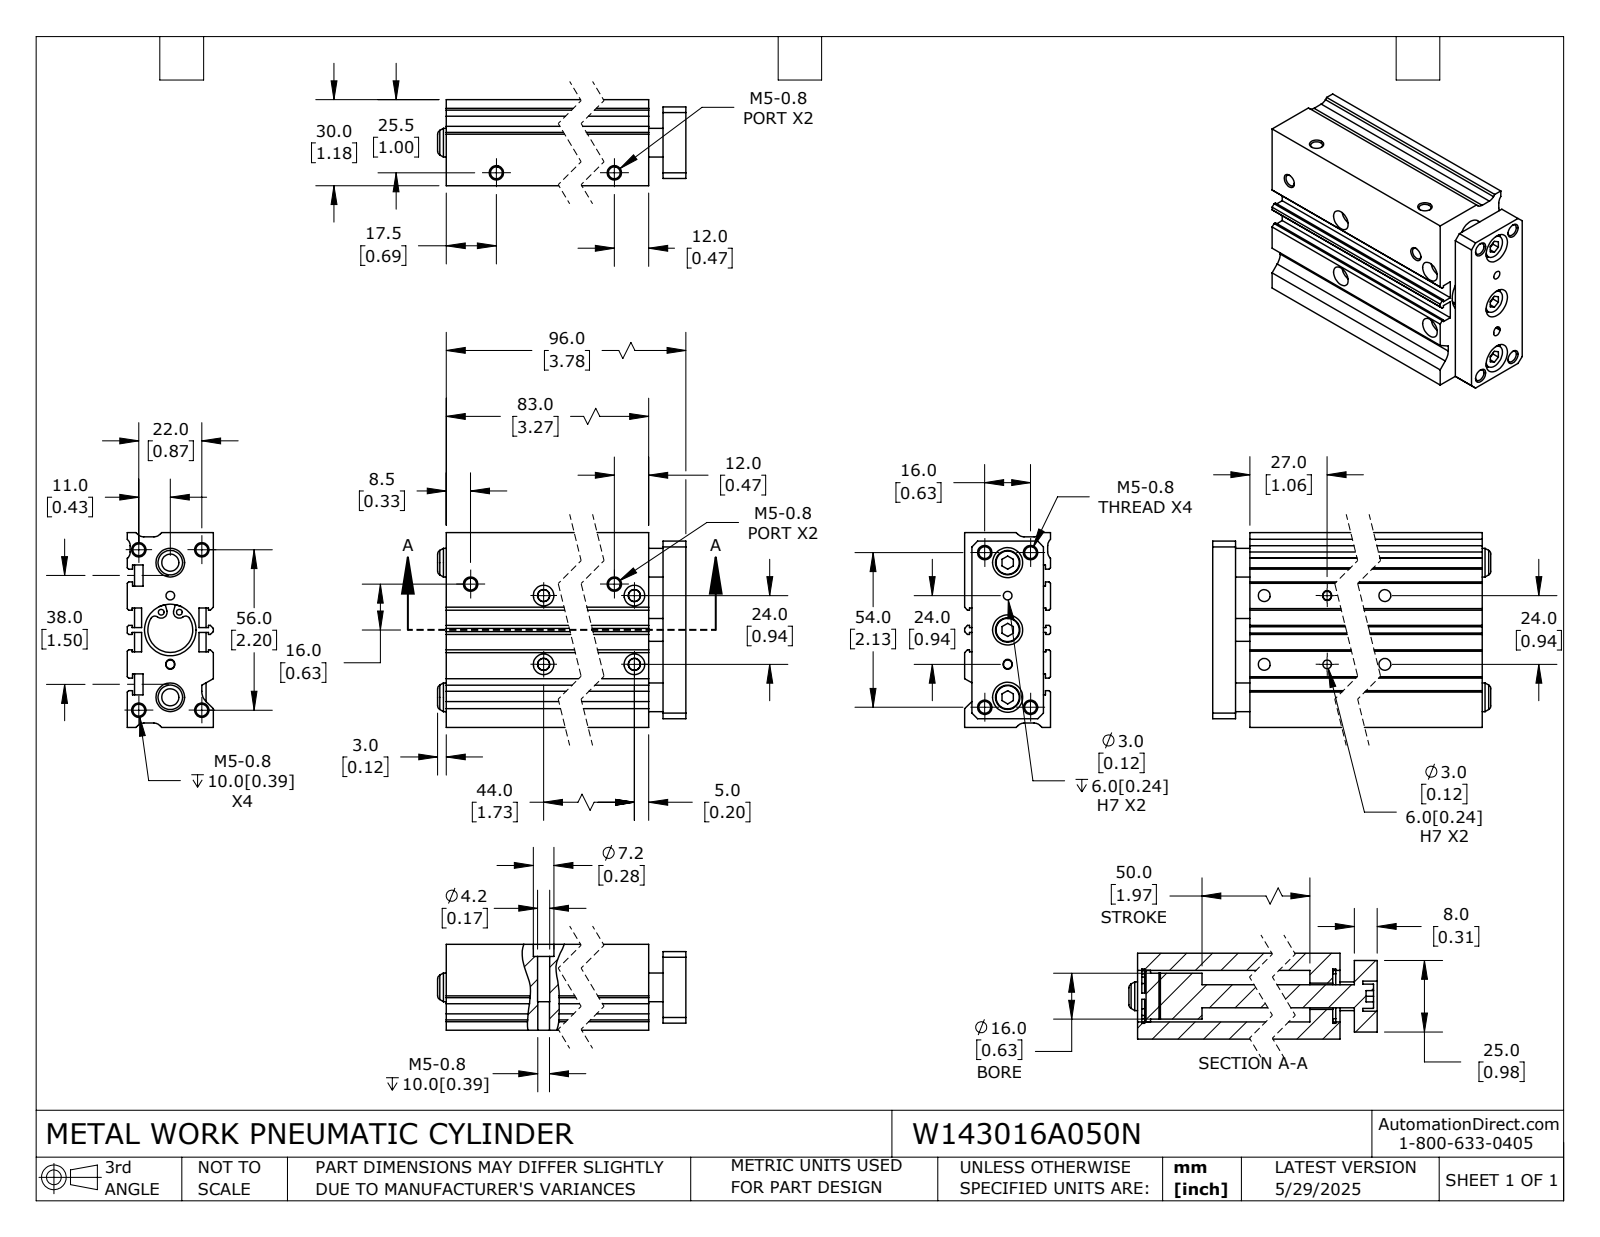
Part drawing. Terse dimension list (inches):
name: W143016A050_ROD; W143016A050_BODY; W143016A050N
written by: SolidWorks 2024 (CONFIG_CONTROL_DESIGN)
unit: in
bodies: 5 solids, 344 faces (169 planar, 137 cylindrical, 38 other)
size: 3.898 × 2.677 × 1.181
volume: 8.856 in³; area: 84.52 in²
holes: 16× ⌀0.163, 4× ⌀0.079, 4× ⌀0.118, 4× ⌀0.165, 4× ⌀0.283, 3× ⌀0.413, 2× ⌀0.394, 1× ⌀0.362, 1× ⌀0.618, 1× ⌀0.709
bosses: 3× ⌀0.335, 2× ⌀0.748, 1× ⌀0.63, 1× ⌀0.315
rounds: 6× R0.118, 4× R0.059, 4× R0.062, 4× R0.081, 1× R0.197
face distances: 0.197, 1.181, 0.984, 0.098, 0.059, 2.677, 0.315, 3.465, 0.02, 0.217
hole spacings: 0.866, 0.124, 0.261, 0.274, 0.344, 0.468, 0.669, 0.693
